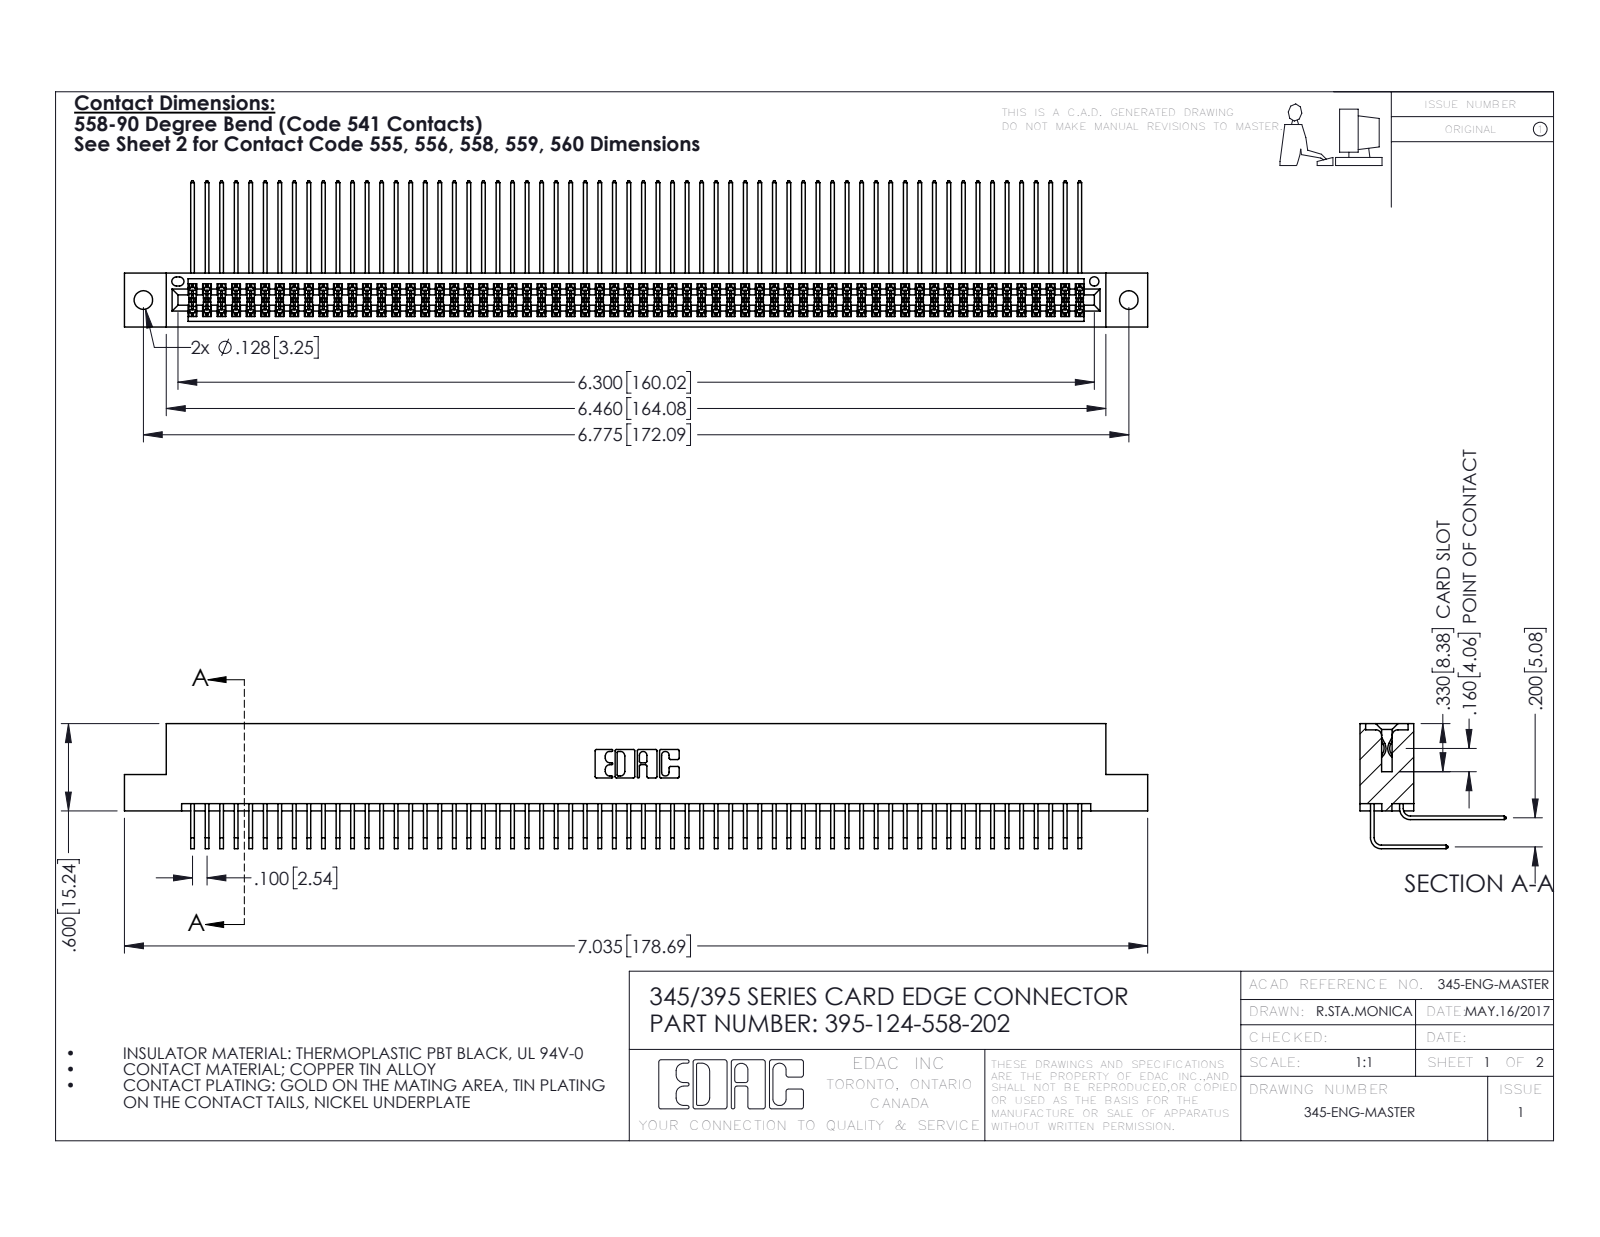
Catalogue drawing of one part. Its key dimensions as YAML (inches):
part_name: "345 Part_Flush Mounting Lugs - 0.128 Dia; 345-292-001_558 Tail - 2; 395-124-558-202; 345-292-001_558 559 Tail - 1"
step_written_by: "SolidWorks 2016 (CONFIG_CONTROL_DESIGN)"
units: inches
bodies: {solids: 125, faces: 6574, planar: 4420, cylindrical: 2154, other: 0}
overall_size: [7.035, 1.005, 0.859]
volume: 1.112
surface_area: 47.14
round_holes:
  - {diameter: 0.128, count: 2}
  - {diameter: 0.064, count: 1}
partial_cylinders:
  - {radius: 0.006, count: 187}
  - {radius: 0.01, count: 22}
  - {radius: 0.007, count: 6}
  - {radius: 0.031, count: 6}
  - {radius: 0.026, count: 3}
  - {radius: 0.014, count: 2}
  - {radius: 0.019, count: 2}
  - {radius: 0.022, count: 2}
face_to_face_distances: [0.072, 0.298, 0.2, 0.37, 0.098, 0.272, 0.025, 0.225, 0.025, 0.175]
hole_center_spacings: [0.27, 6.539, 6.775]
